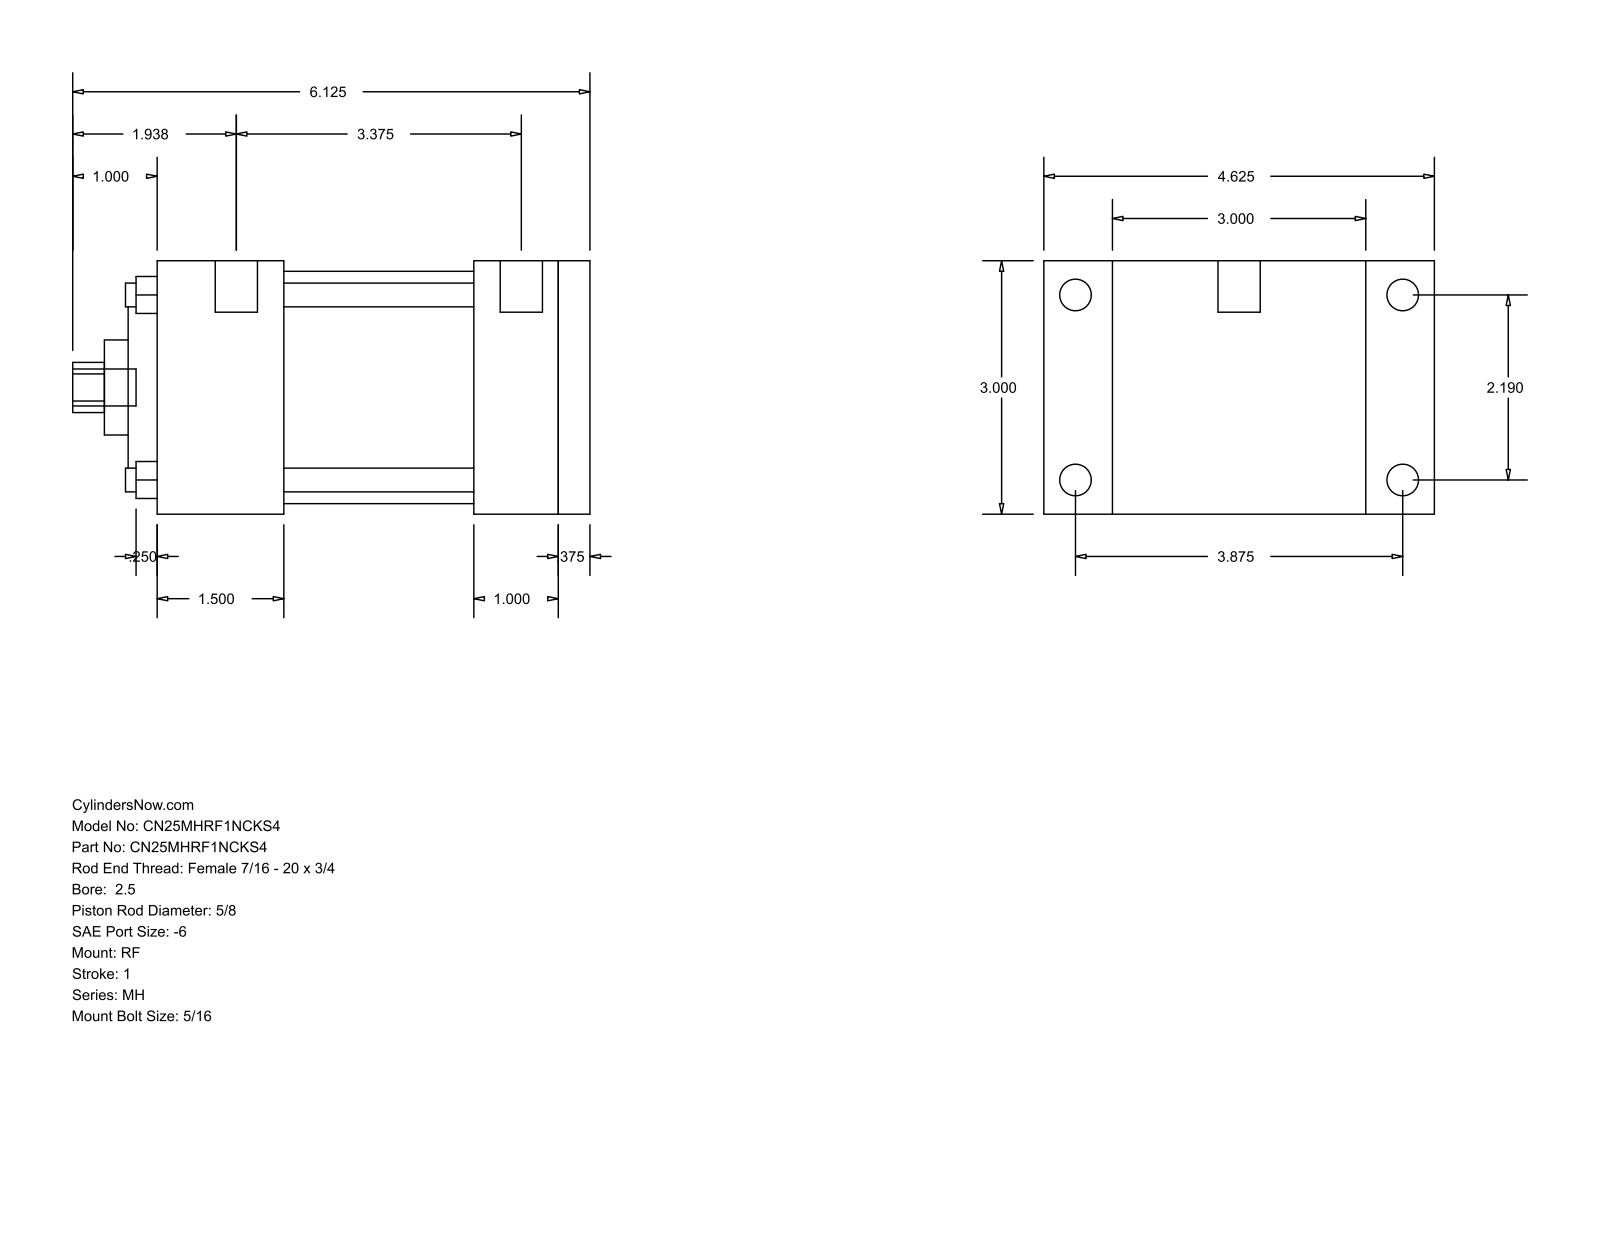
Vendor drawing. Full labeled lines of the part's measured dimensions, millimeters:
Part name (STEP PRODUCT): MH_RF__0250_0.625
STEP written by: GSSL Pune (CONFIG_CONTROL_DESIGN)
Units: millimetres
Bodies: 0 solids, 94 faces (65 planar, 29 cylindrical, 0 other)
Overall size (bounding box): 155.57 × 117.47 × 76.2
Round holes (diameter × count): ⌀7.14 ×4, ⌀15.88 ×1, ⌀28.57 ×1, ⌀55.55 ×1, ⌀69.85 ×1
Round bosses / shafts (diameter × count): ⌀9.53 ×4, ⌀5.56 ×4, ⌀12.7 ×2, ⌀11.11 ×1
Partial cylindrical surfaces — rounded edges, fillets, slot ends (radius × count): R7.54 ×1
Main face-to-face distances: 76.2, 9.52, 130.17, 120.65, 25.4, 57.15, 95.25, 34.92, 38.1, 82.55
Hole centre spacings: 39.33, 55.62, 78.66
